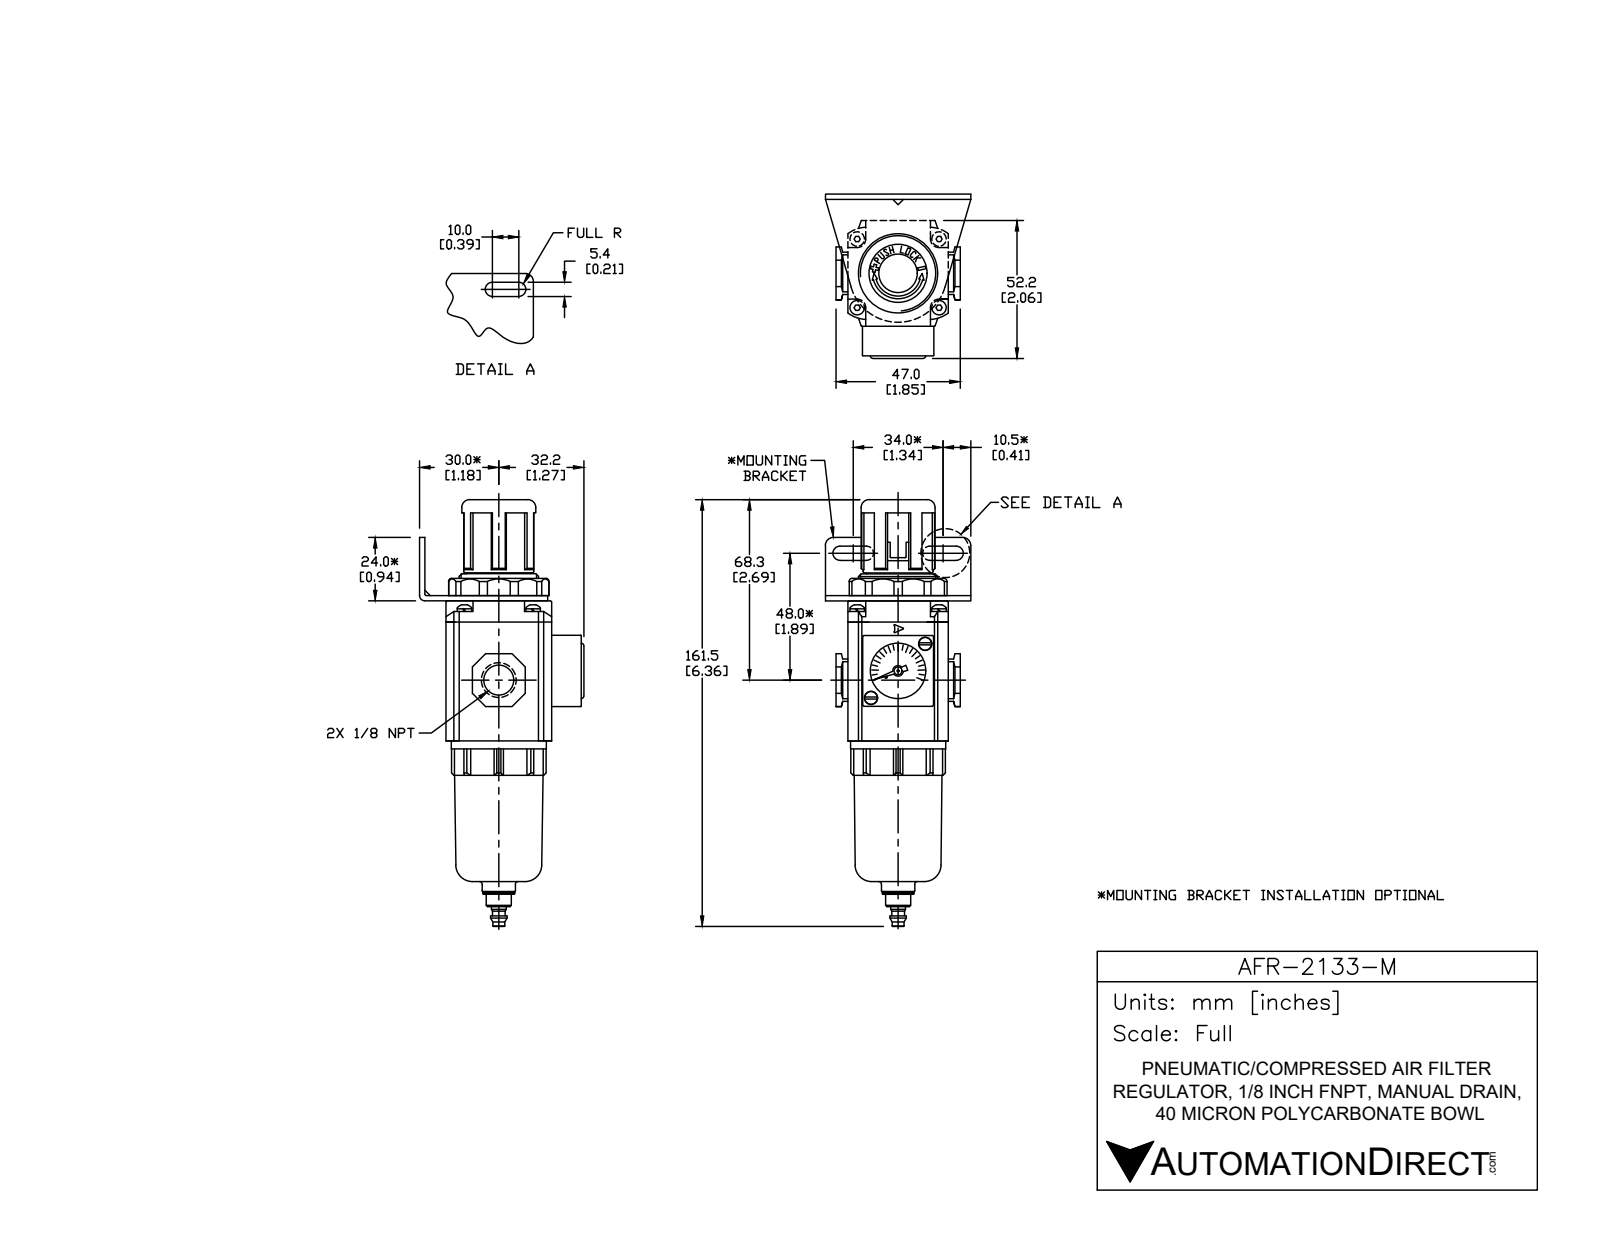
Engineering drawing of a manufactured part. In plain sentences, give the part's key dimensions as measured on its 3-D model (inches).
The part is named "AFR-2133-M". Its 3-D file was written by "SolidWorks 2015 (CONFIG_CONTROL_DESIGN)". It is 15 solids with 548 faces: 329 planar, 159 cylindrical and 60 other. Overall it measures 6.346 by 2.441 by 2.165 inches. Its volume is 8.244 cubic inches and its surface area 62.1 square inches. Round holes: 7 of diameter 0.118, 1 of diameter 0.079, 1 of diameter 0.332, 1 of diameter 0.827, 1 of diameter 0.866, 1 of diameter 1.004, 1 of diameter 1.181. Round bosses or shafts: 4 of diameter 0.217, 2 of diameter 0.106, 1 of diameter 1.102, 1 of diameter 1.024, 1 of diameter 0.937, 1 of diameter 0.551, 1 of diameter 0.496, 1 of diameter 0.472. Partial cylindrical surfaces (rounded edges, fillets, slot ends): 12 of radius 0.039, 10 of radius 0.047, 6 of radius 0.128, 4 of radius 0.012, 4 of radius 0.108, 4 of radius 0.472, 3 of radius 0.008, 1 of radius 0.079. The main face-to-face distances are 0.079, 2.165, 1.575, 2.087, 1.496, 1.535, 0.394, 0.039, 1.969, 0.433. The hole center spacings are 0.796, 0.571, 1.024, 1.22, 1.593, 1.141.
